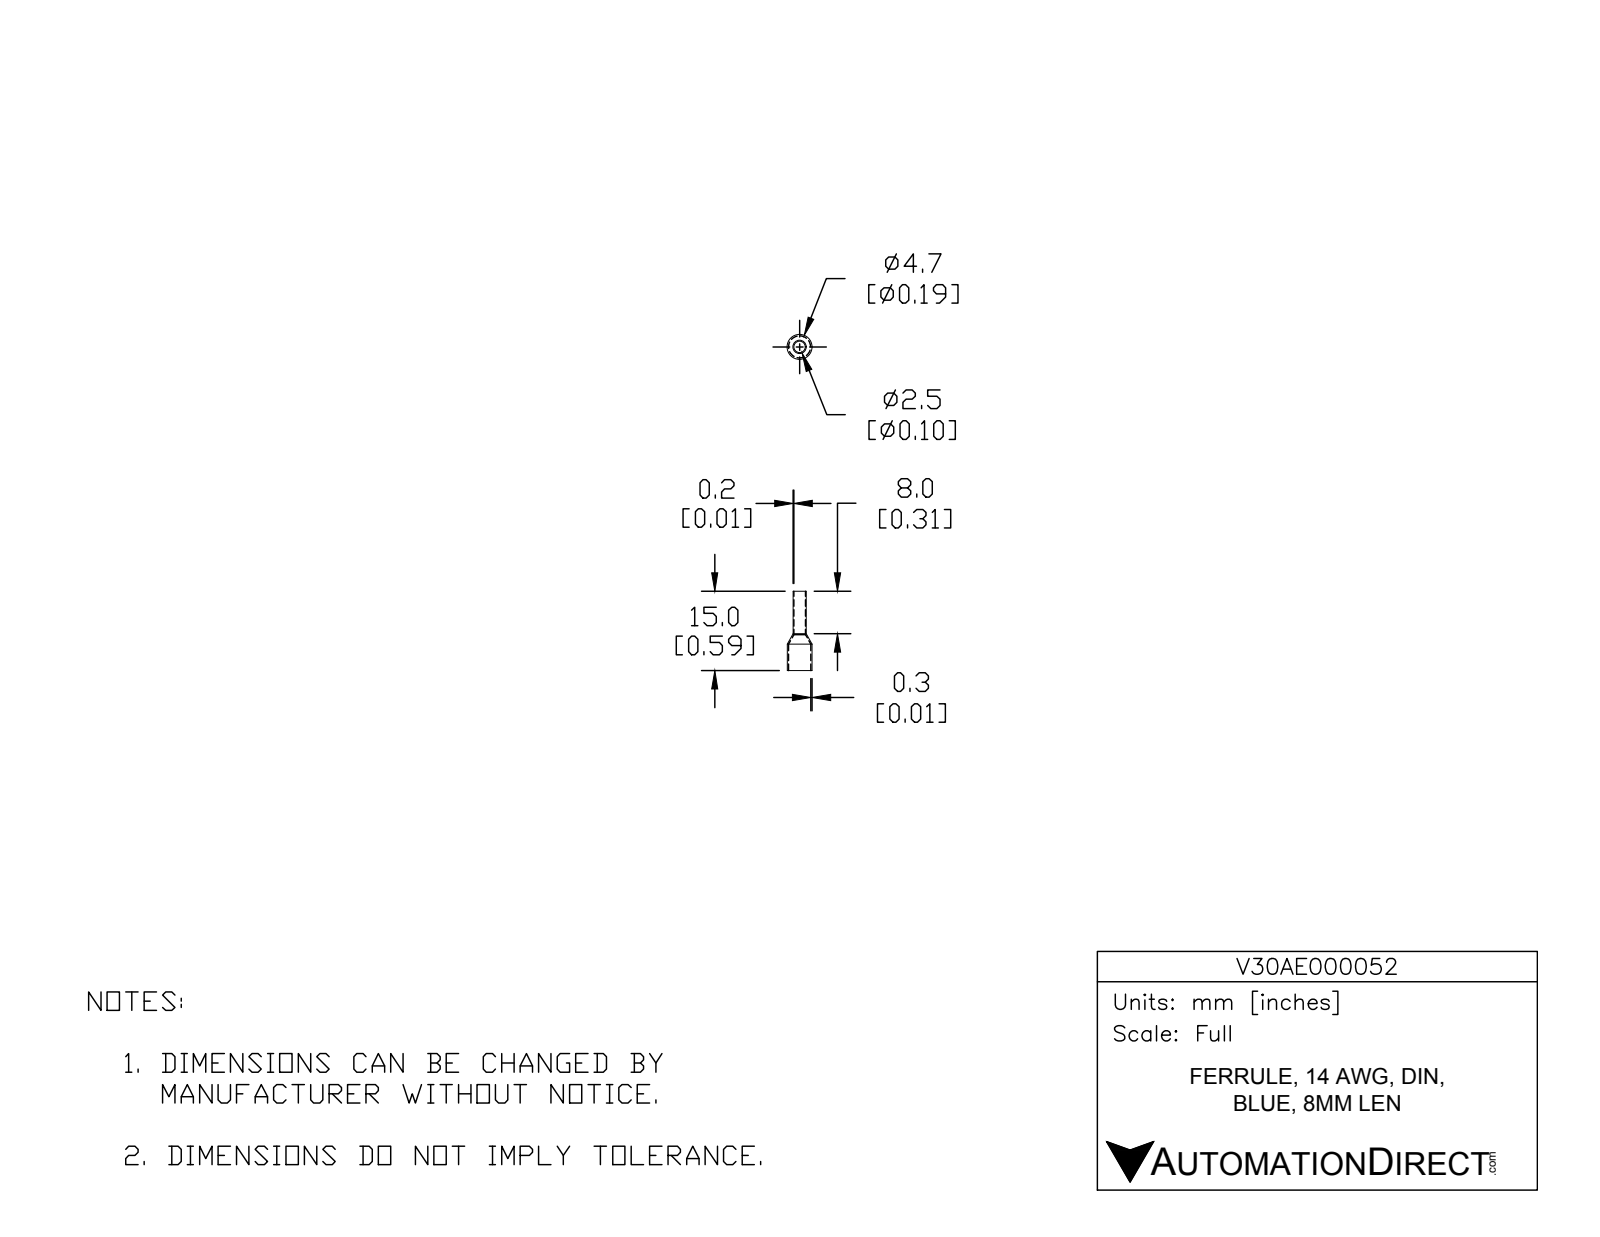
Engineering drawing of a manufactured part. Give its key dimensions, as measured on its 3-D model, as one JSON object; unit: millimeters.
{"part_name": "V30AE000052", "step_written_by": "SolidWorks 2017 (AUTOMOTIVE_DESIGN)", "units": "millimeters", "bodies": {"solids": 1, "faces": 14, "planar": 2, "cylindrical": 8, "other": 4}, "overall_size": [15, 4.7, 4.7], "volume_mm3": 32, "surface_area_mm2": 310, "round_holes": [[2.2, 1], [4.2, 1]], "round_bosses_or_shafts": [[4.7, 1], [2.5, 1]], "face_to_face_distances": [15]}
